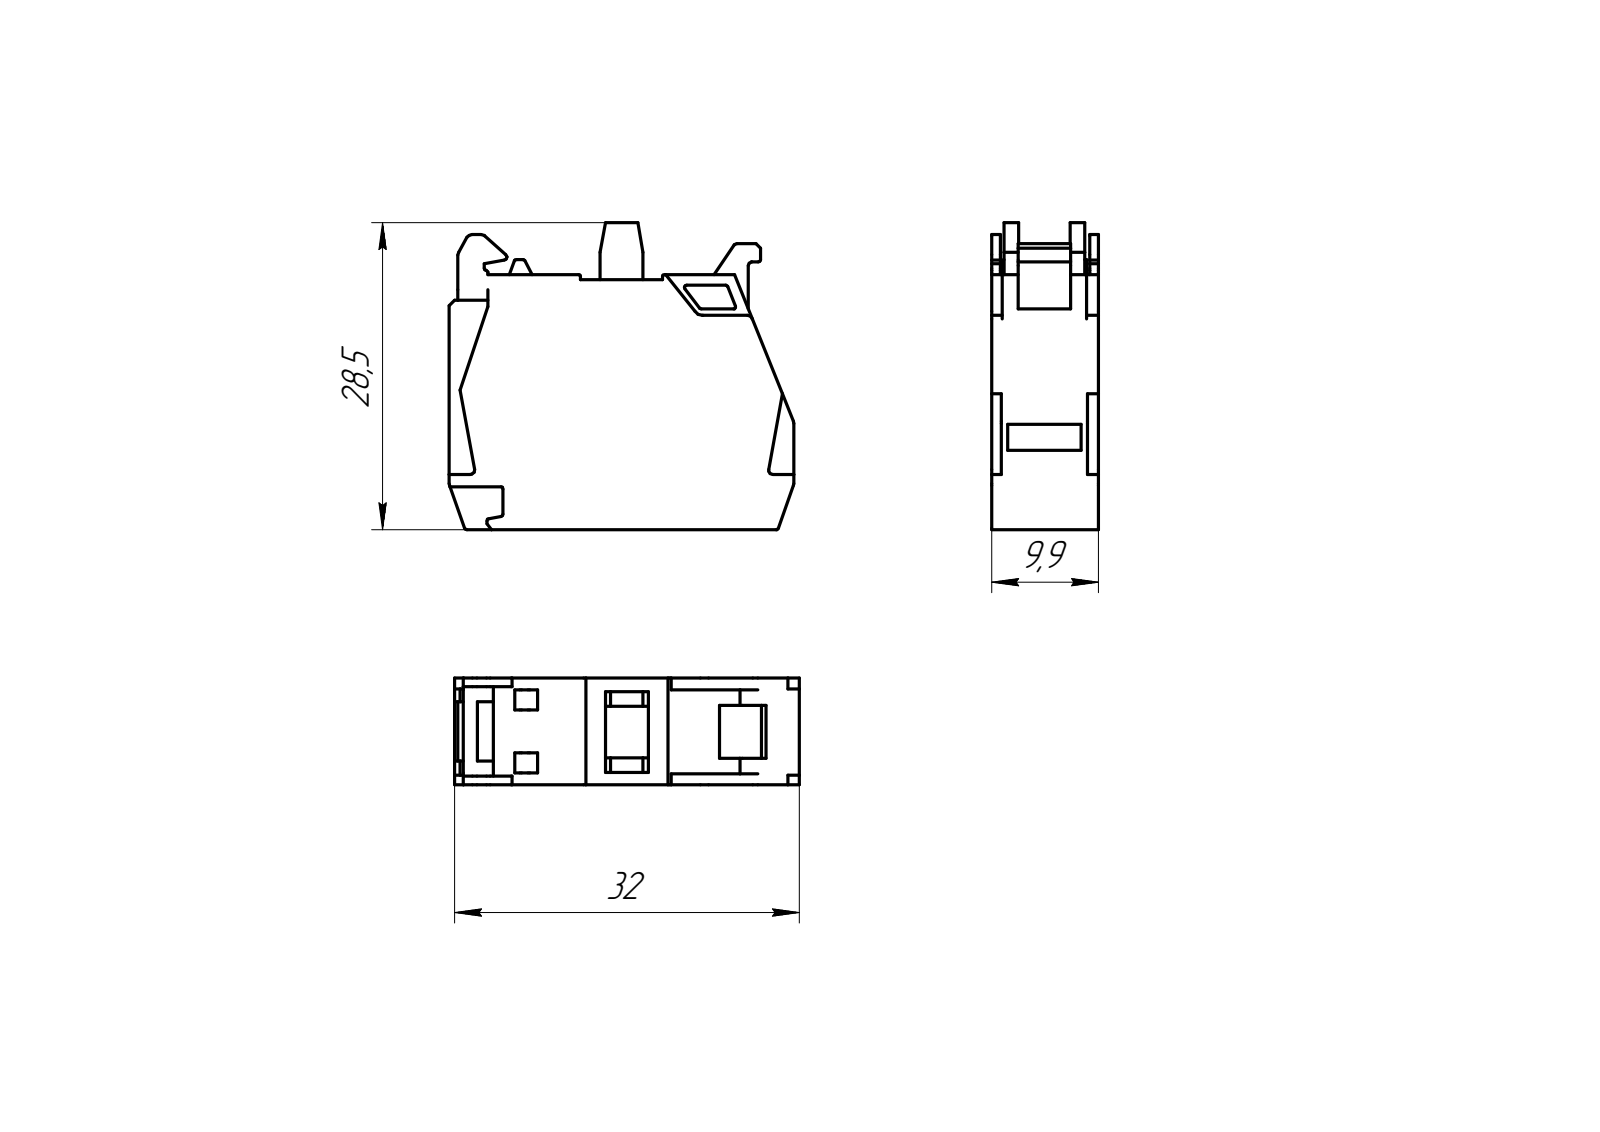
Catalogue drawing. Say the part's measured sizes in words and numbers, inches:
Its 3-D file was written by "PRO/ENGINEER BY PARAMETRIC TECHNOLOGY CORPORATION, 2010280 (CONFIG_CONTROL_DESIGN)". It is 1 solid with 193 faces: 141 planar, 52 cylindrical and 0 other. Overall it measures 1.26 by 1.122 by 0.39 inches. Its volume is 0.392 cubic inches and its surface area 4.858 square inches. Partial cylindrical surfaces (rounded edges, fillets, slot ends): 16 of radius 0.008, 7 of radius 0.02, 5 of radius 0.012, 3 of radius 0.039, 2 of radius 0.016. The main face-to-face distances are 0.39, 0.039, 0.059, 0.933, 0.291, 0.815, 0.035, 0.094, 0.256, 0.295.
